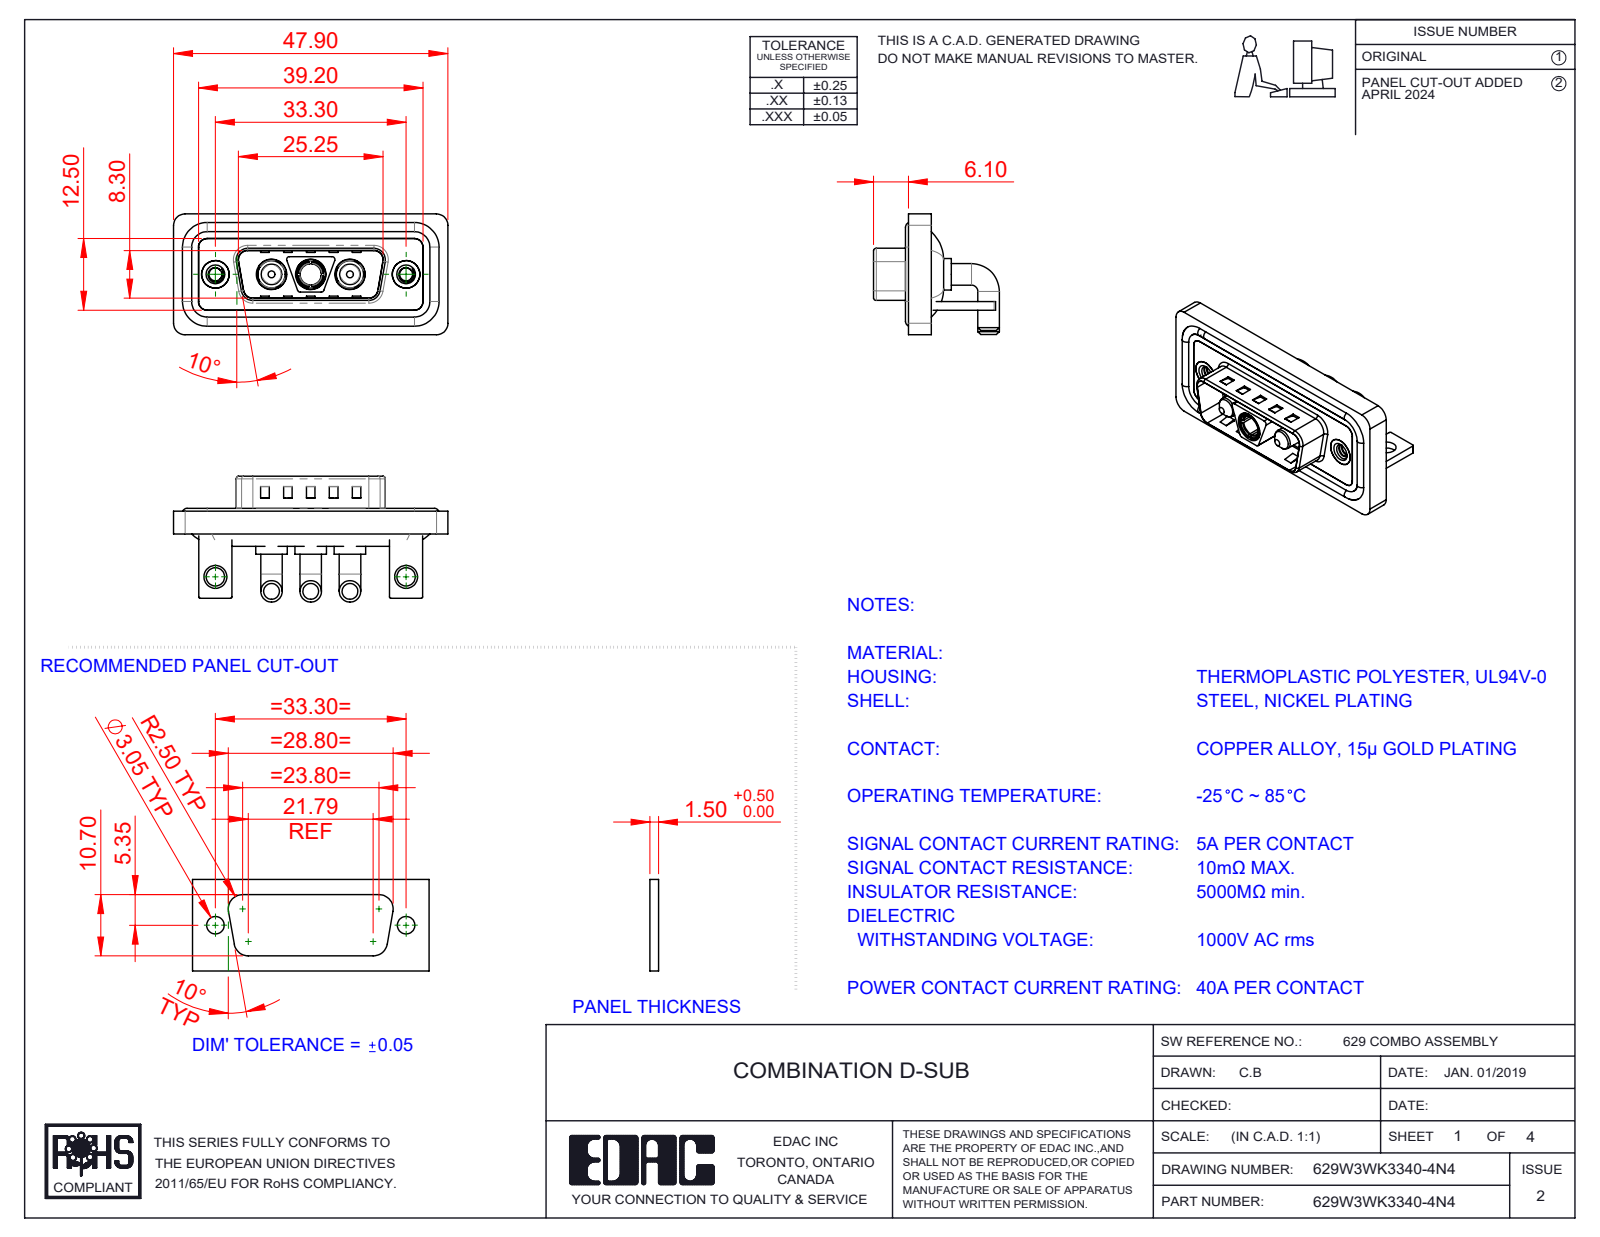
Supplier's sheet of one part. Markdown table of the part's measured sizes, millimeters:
| quantity | value |
| --- | --- |
| part name | Power Pin_40A RA; 629Combo Stabilizer Bracket; 629Combo Waterproof Housing_15 Contacts; 629W3WK3340-4N4 (+5 more) |
| STEP written by | SolidWorks 2023 (CONFIG_CONTROL_DESIGN) |
| units | millimeters |
| bodies | 15 solids, 661 faces (251 planar, 274 cylindrical, 136 other) |
| overall size | 47.9 × 21.98 × 21.1 |
| volume | 6 385 mm³ |
| surface area | 10 136 mm² |
| round holes (diameter × count) | 4.85 × 3, 5.3 × 3, 2.26 × 2, 3.2 × 2, 4 × 2, 4.8 × 2, 5 × 2, 3.7 × 1 |
| round bosses / shafts (diameter × count) | 3.75 × 6, 1.6 × 4, 5.5 × 3, 5.2 × 3, 4.75 × 3, 4.9 × 2, 3.6 × 2, 4.96 × 1 |
| partial cylindrical surfaces (radius × count) | 2 × 21, 1.5 × 18, 0.25 × 16, 0.5 × 13, 1.6 × 8, 0.6 × 4, 0.65 × 4, 0.9 × 4 |
| main face-to-face distances | 0.4, 1.5, 0.8, 2.9, 1.1, 2.1, 3.7, 1.6, 1.2, 4.5 |
| hole center spacings | 6.85, 9.8, 16.65, 23.5, 33.3, 13.7 |
